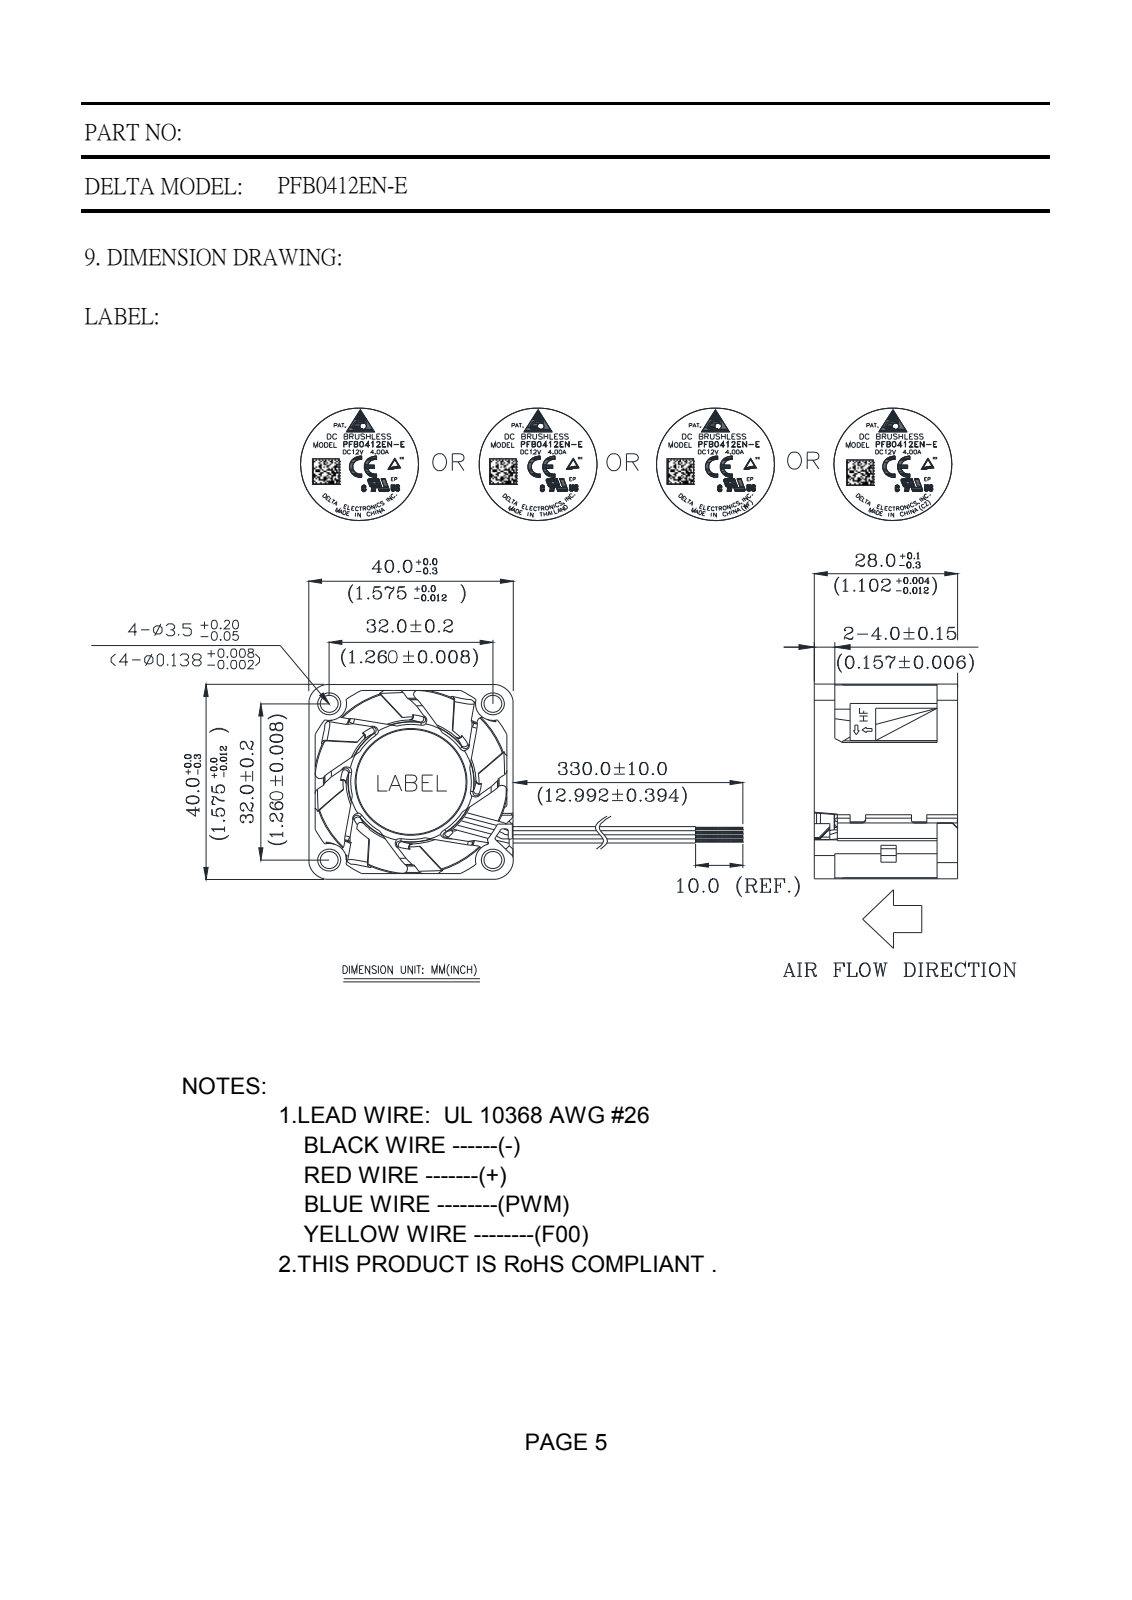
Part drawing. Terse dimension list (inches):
name: PFB0412EN-E
written by: PRO/ENGINEER BY PARAMETRIC TECHNOLOGY CORPORATION, 2009360 (CONFIG_CONTROL_DESIGN)
unit: in
bodies: 3 solids, 442 faces (223 planar, 120 cylindrical, 99 other)
size: 1.858 × 1.858 × 1.102
volume: 1.385 in³; area: 25.3 in²
holes: 4× ⌀0.138, 1× ⌀1.48
bosses: 1× ⌀0.984
rounds: 14× R0.008, 10× R0.016, 10× R0.039, 4× R0.02, 4× R0.126, 4× R0.128, 4× R0.134, 4× R0.148
face distances: 1.571, 0.197, 1.563, 0.098, 0.039, 0.295, 0.047, 1.524, 1.516, 0.02
hole spacings: 0.891, 1.26, 1.782
